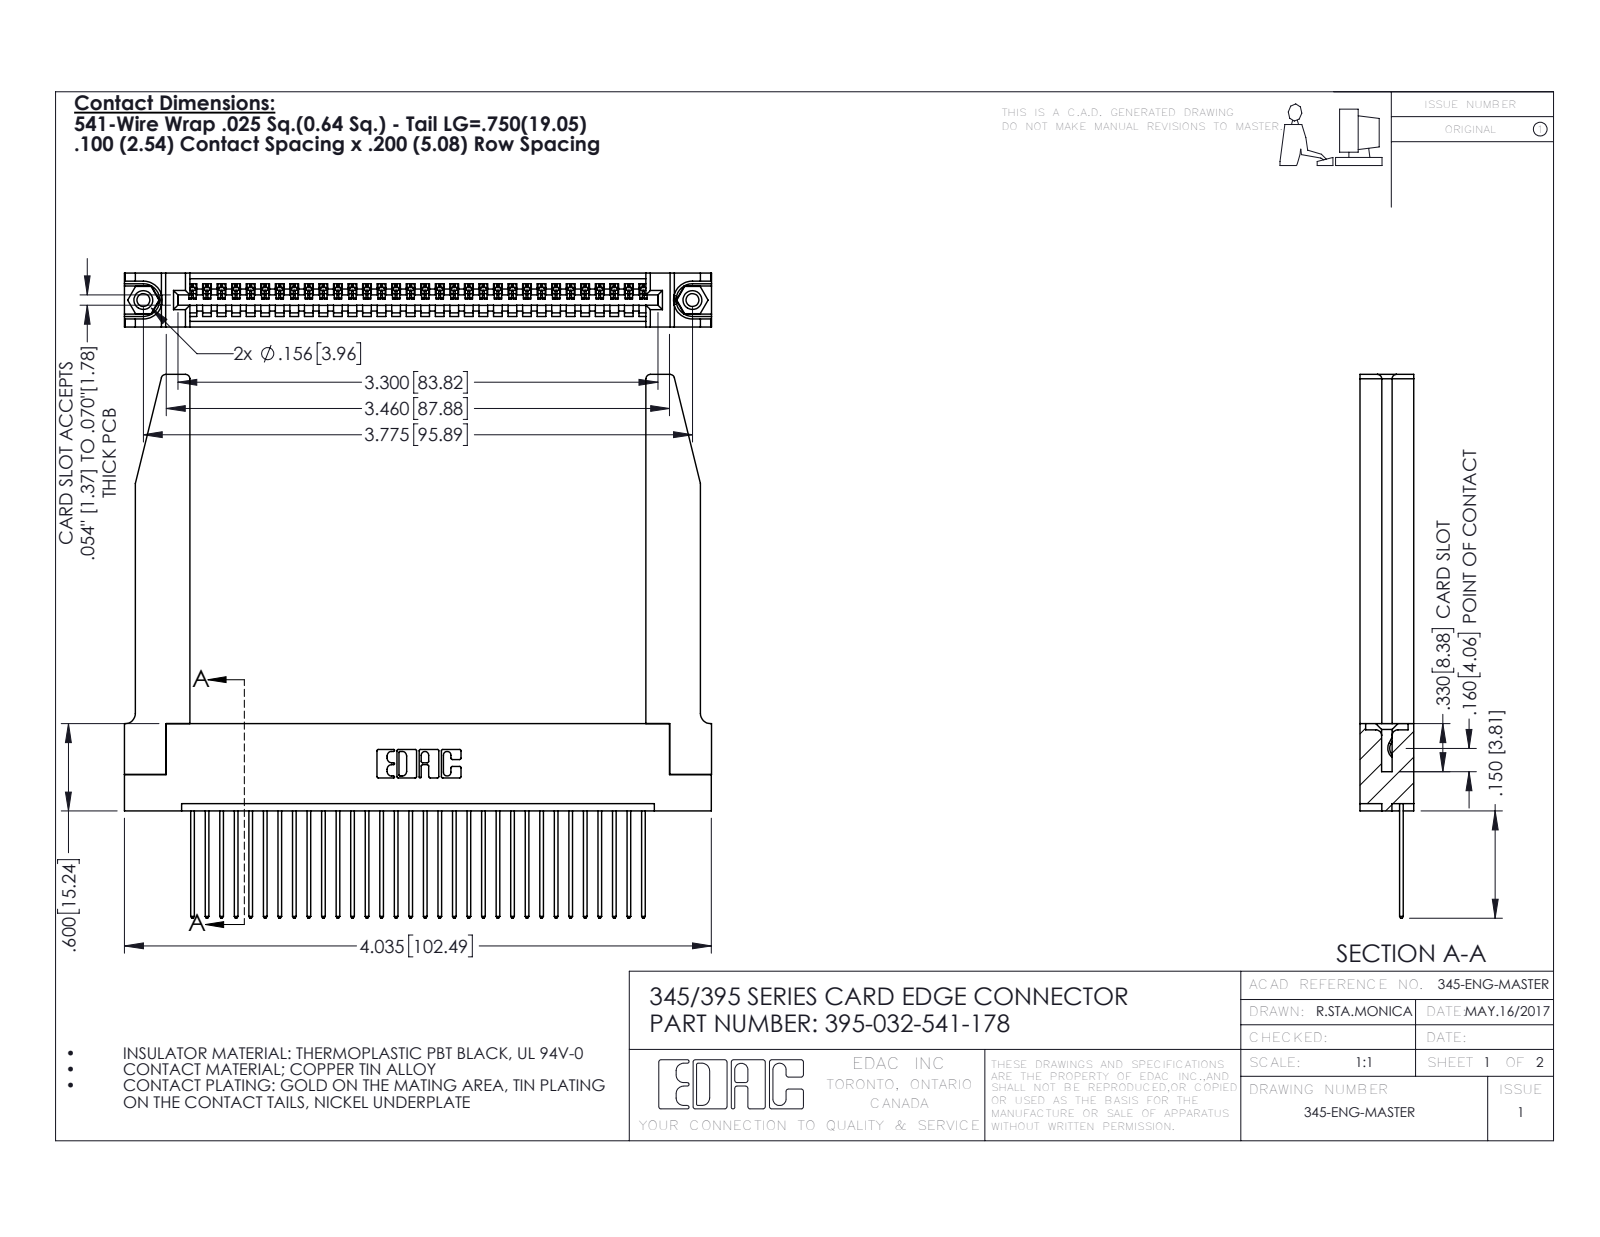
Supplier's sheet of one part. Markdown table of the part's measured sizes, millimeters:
| quantity | value |
| --- | --- |
| part name | 395-032-541-178; 345-250-001_345-250-001-102; 345-292-001_345-293-141; 345-220-078_345-220-078 (+1 more) |
| STEP written by | SolidWorks 2016 (CONFIG_CONTROL_DESIGN) |
| units | millimeters |
| bodies | 37 solids, 2216 faces (1502 planar, 662 cylindrical, 52 other) |
| overall size | 102.5 × 94.9 × 9.4 |
| volume | 17 530 mm³ |
| surface area | 20 300 mm² |
| round holes (diameter × count) | 2.3 × 2, 3.2 × 2, 4 × 2, 1.6 × 1 |
| round bosses / shafts (diameter × count) | 3.9 × 2 |
| partial cylindrical surfaces (radius × count) | 0.2 × 64, 0.3 × 64, 0.3 × 22, 0.8 × 8, 0.2 × 6, 0.8 × 6, 0.7 × 3, 0.8 × 2 |
| main face-to-face distances | 9.4, 1.8, 7.6, 5.1, 2.5, 6.9, 0.6, 3.8, 3.8, 5.7 |
| hole center spacings | 6.9, 89.9, 95.9 |
